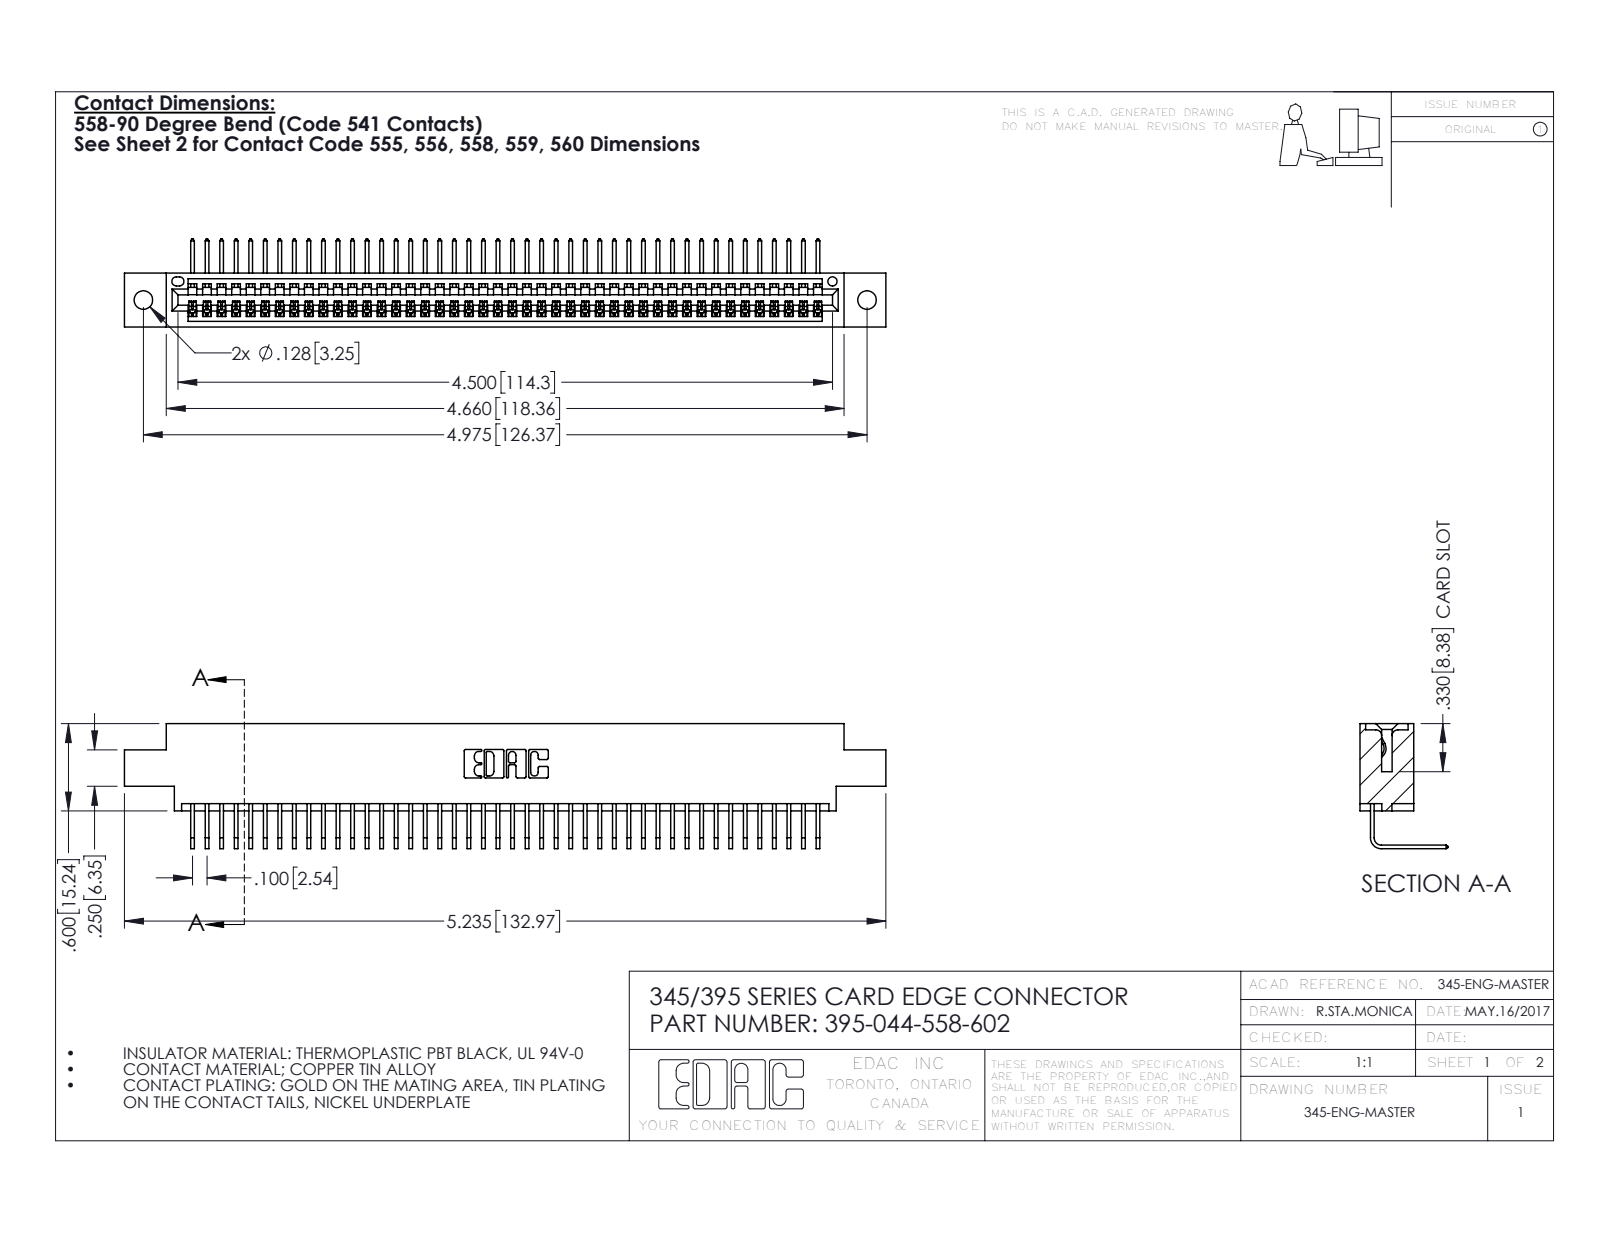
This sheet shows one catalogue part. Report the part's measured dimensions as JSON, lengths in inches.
{"part_name": "345-292-001_558 Tail - 2; 345 Part_0.170 Offset - 0.128 Dia; 395-044-558-602", "step_written_by": "SolidWorks 2016 (CONFIG_CONTROL_DESIGN)", "units": "inches", "bodies": {"solids": 45, "faces": 2770, "planar": 1932, "cylindrical": 838, "other": 0}, "overall_size": [5.235, 0.859, 0.605], "volume_in3": 0.771, "surface_area_in2": 27.19, "round_holes": [[0.128, 2], [0.064, 1]], "partial_cylinders_radius": [[0.006, 88], [0.01, 22], [0.007, 6], [0.031, 6], [0.026, 3], [0.031, 2], [0.04, 2], [0.014, 1]], "face_to_face_distances": [0.072, 0.298, 0.37, 0.2, 0.098, 0.272, 0.025, 0.225, 0.175, 0.149], "hole_center_spacings": [0.27, 4.739, 4.975]}
